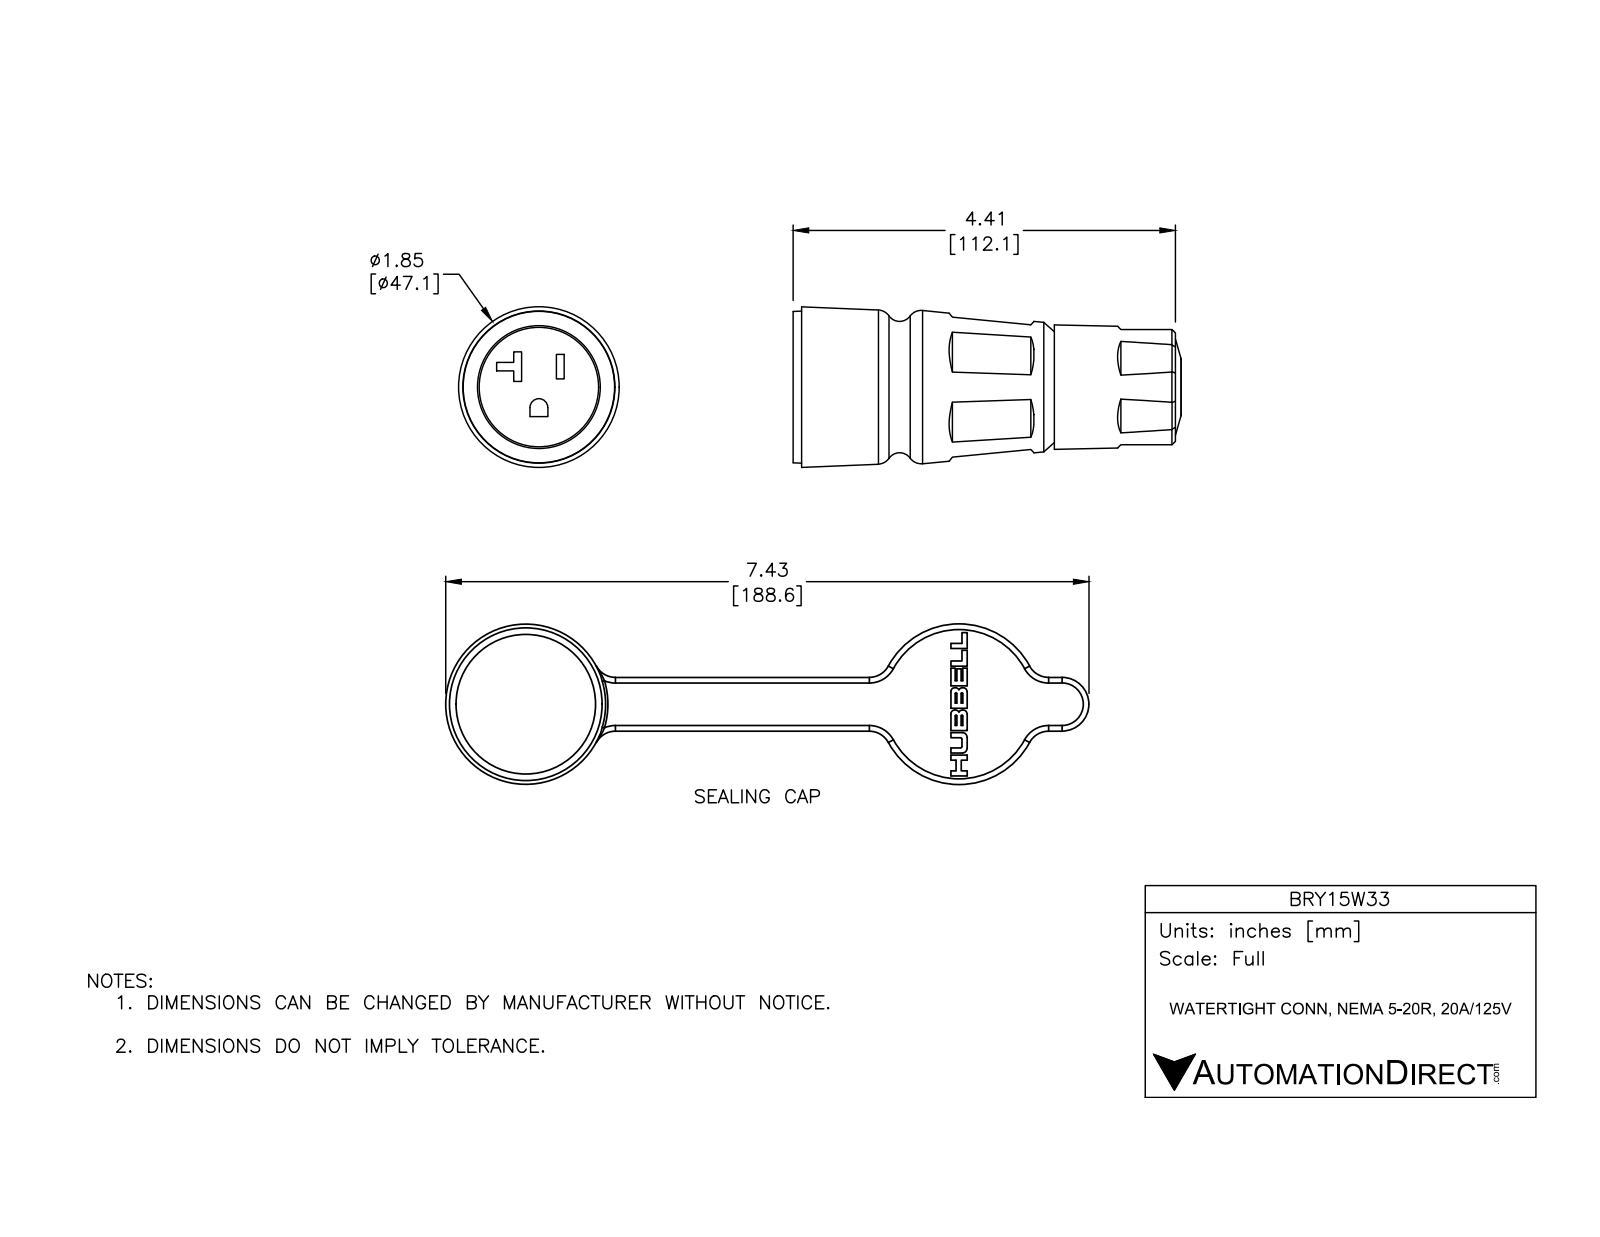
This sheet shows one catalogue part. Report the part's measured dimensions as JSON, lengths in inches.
{"part_name": "BRY15W33-CONNECTOR; BRY15W-CAP; BRY15W33", "step_written_by": "SolidWorks 2016 (AUTOMOTIVE_DESIGN)", "units": "inches", "bodies": {"solids": 5, "faces": 185, "planar": 83, "cylindrical": 46, "other": 56}, "overall_size": [7.364, 4.479, 1.854], "volume_in3": 8.191, "surface_area_in2": 73.66, "round_holes": [[0.561, 1], [1.112, 1], [1.22, 1], [1.417, 1], [1.535, 1]], "round_bosses_or_shafts": [[1.85, 1], [1.772, 1], [1.665, 1], [1.472, 1], [1.378, 1], [0.993, 1]], "partial_cylinders_radius": [[0.059, 4], [0.236, 4], [0.157, 2], [0.103, 1], [0.315, 1]], "face_to_face_distances": [0.128, 0.202, 0.33, 0.866, 0.664, 0.536, 0.22, 0.093, 0.03, 0.422], "hole_center_spacings": [4.941]}
